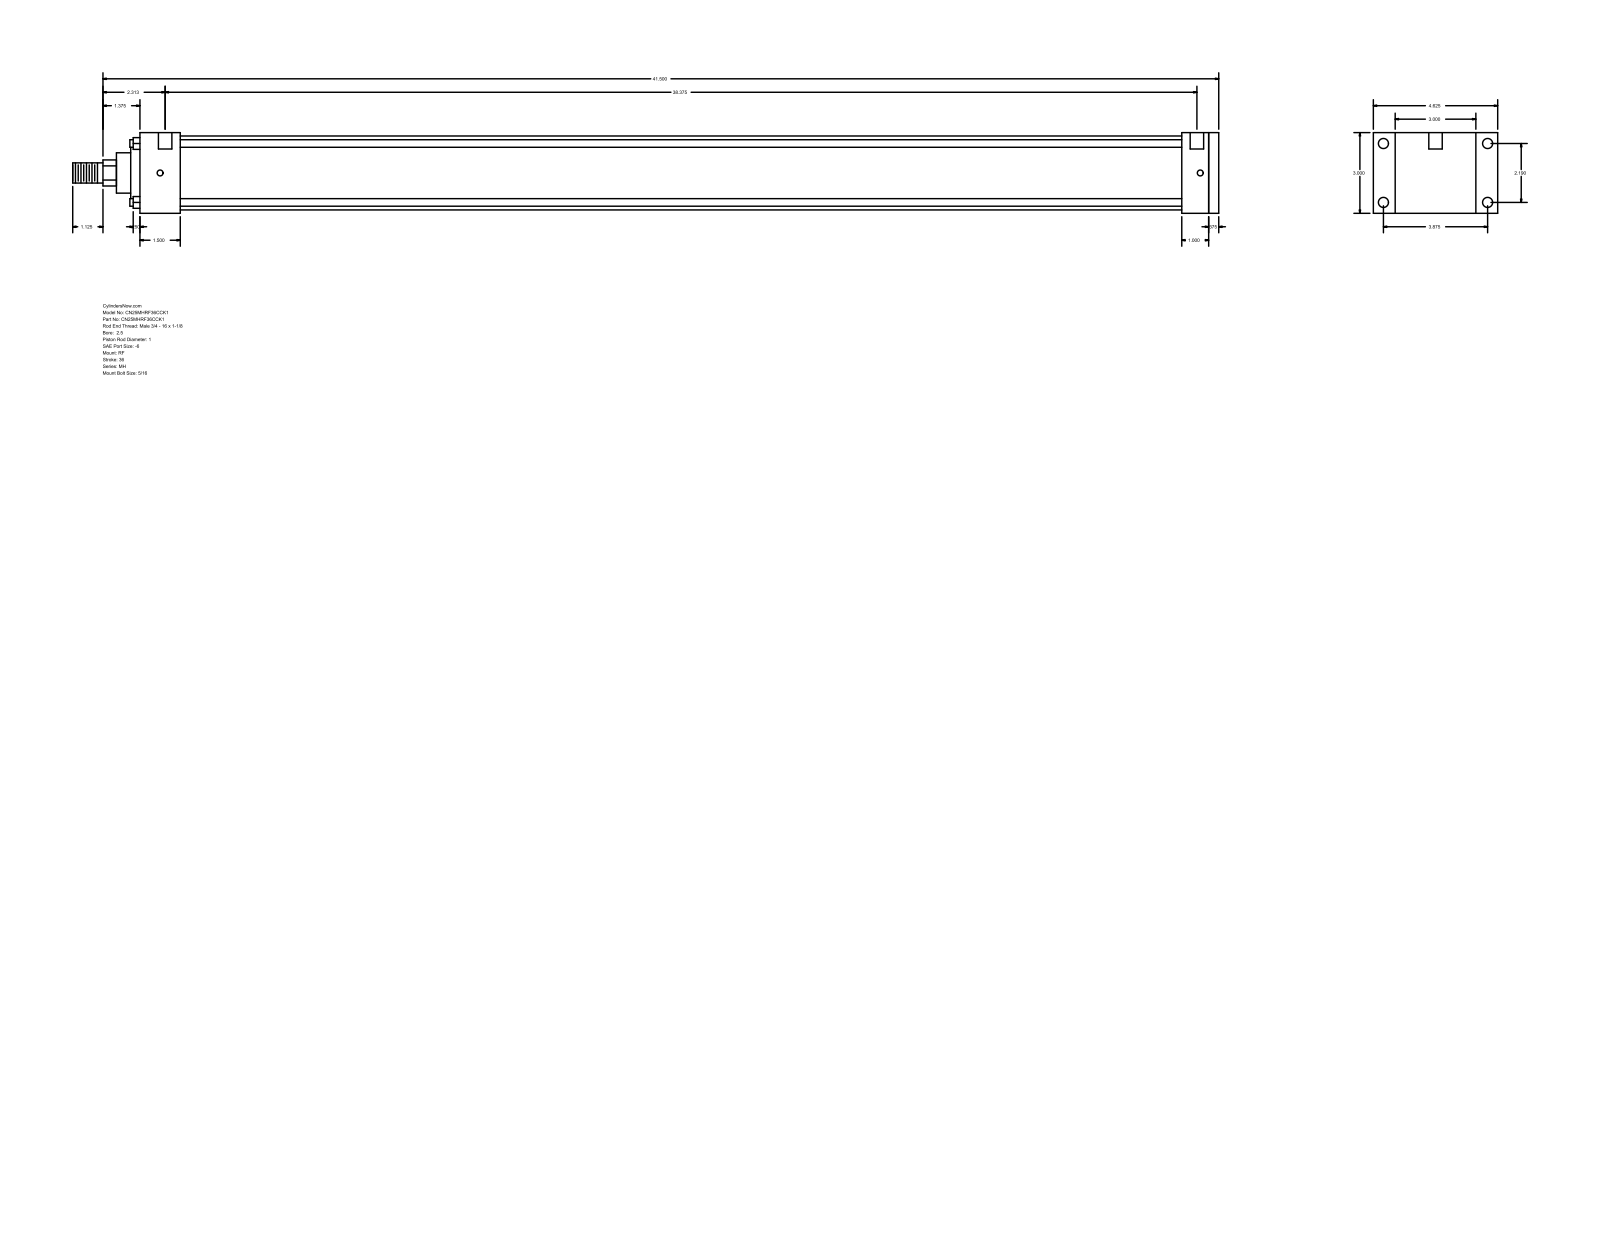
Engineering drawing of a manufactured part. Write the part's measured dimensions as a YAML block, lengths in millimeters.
part_name: "MH_RF__0250_1"
step_written_by: "GSSL Pune (CONFIG_CONTROL_DESIGN)"
units: millimeters
bodies: {solids: 0, faces: 94, planar: 65, cylindrical: 29, other: 0}
overall_size: [1082.67, 117.47, 76.2]
round_holes:
  - {diameter: 5.56, count: 4}
  - {diameter: 9.53, count: 4}
  - {diameter: 12.7, count: 2}
round_bosses_or_shafts:
  - {diameter: 7.14, count: 4}
  - {diameter: 69.85, count: 1}
  - {diameter: 60.33, count: 1}
  - {diameter: 38.1, count: 1}
  - {diameter: 25.4, count: 1}
  - {diameter: 19.05, count: 1}
partial_cylinders:
  - {radius: 12.29, count: 1}
face_to_face_distances: [76.2, 9.52, 1019.18, 1009.66, 984.25, 25.41, 34.93, 38.11, 946.14, 971.55]
hole_center_spacings: [55.62, 98.42, 113.05, 982.66, 3.18, 4.76, 974.72, 977.9]
